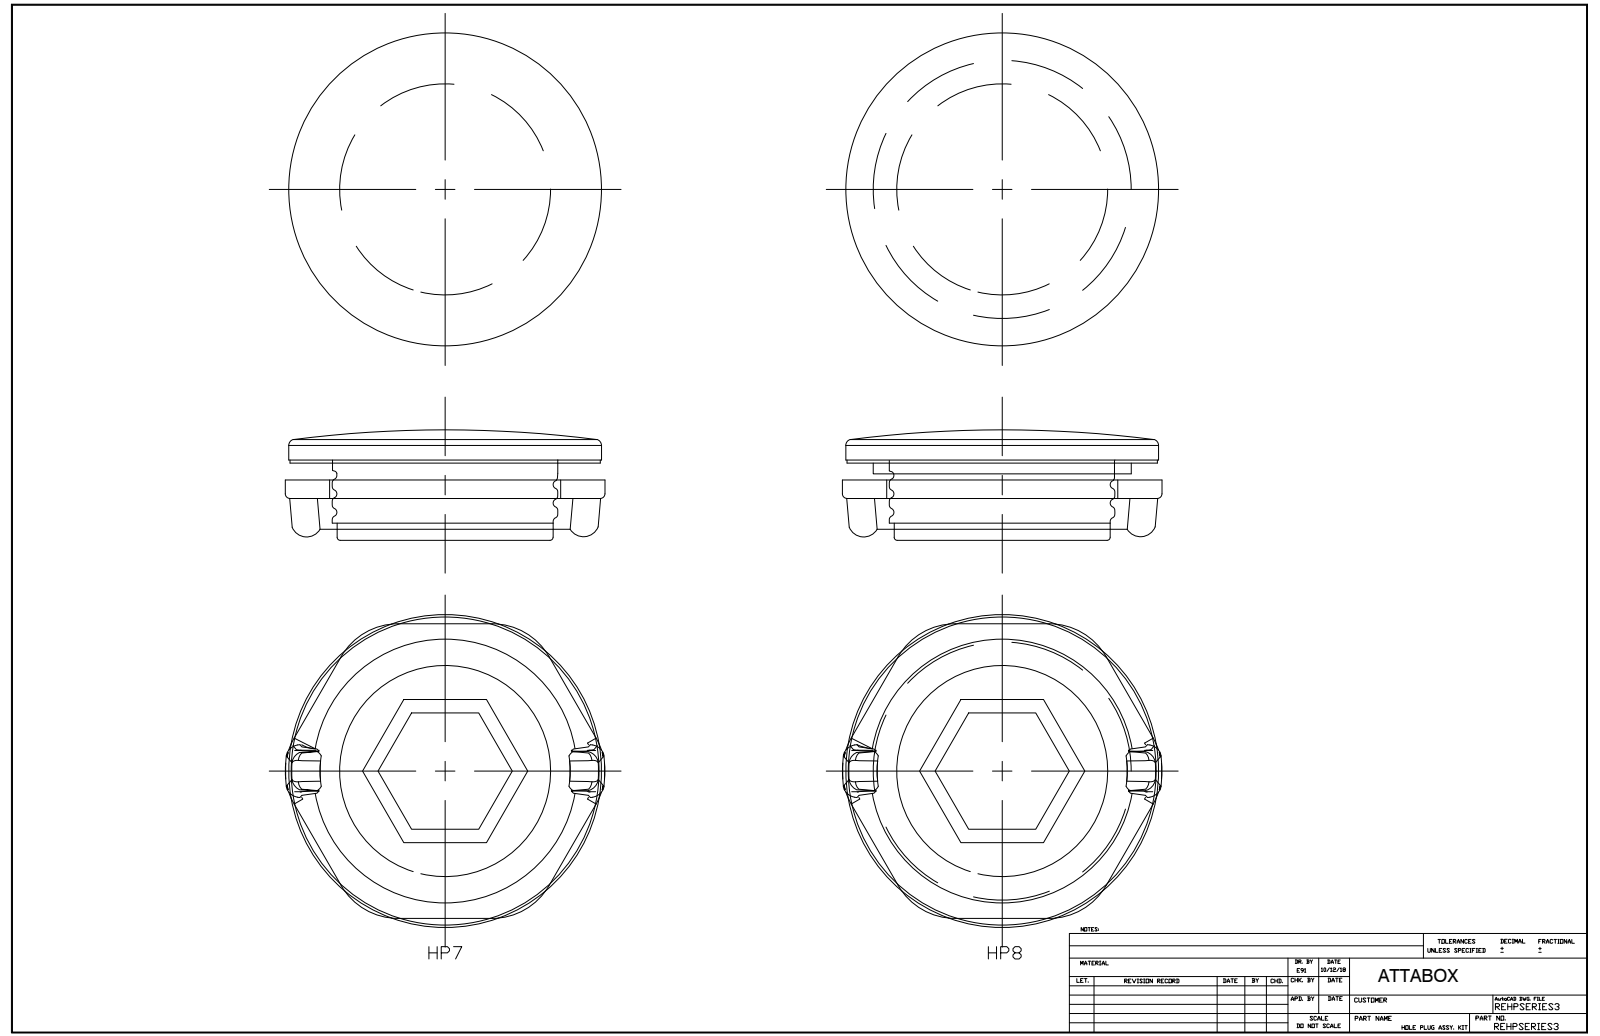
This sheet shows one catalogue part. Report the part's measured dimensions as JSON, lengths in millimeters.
{"part_name": "HPSERIES3", "step_written_by": "SolidWorks 2018 (AUTOMOTIVE_DESIGN)", "units": "millimeters", "bodies": {"solids": 3, "faces": 151, "planar": 32, "cylindrical": 49, "other": 70}, "overall_size": [53.5, 50.8, 19.9], "volume_mm3": 23550, "surface_area_mm2": 13540, "round_holes": [[34.3, 1], [35.3, 1]], "round_bosses_or_shafts": [[50.8, 1], [50.3, 1], [32.8, 1]], "partial_cylinders_radius": [[0.8, 14], [0.2, 8], [2, 8], [5, 6], [0.2, 4], [3, 2], [0.5, 1]], "face_to_face_distances": [5.7, 3.2, 5.4, 2.3, 2.5, 7.8, 10.9, 13.2, 13.5, 4.7]}
